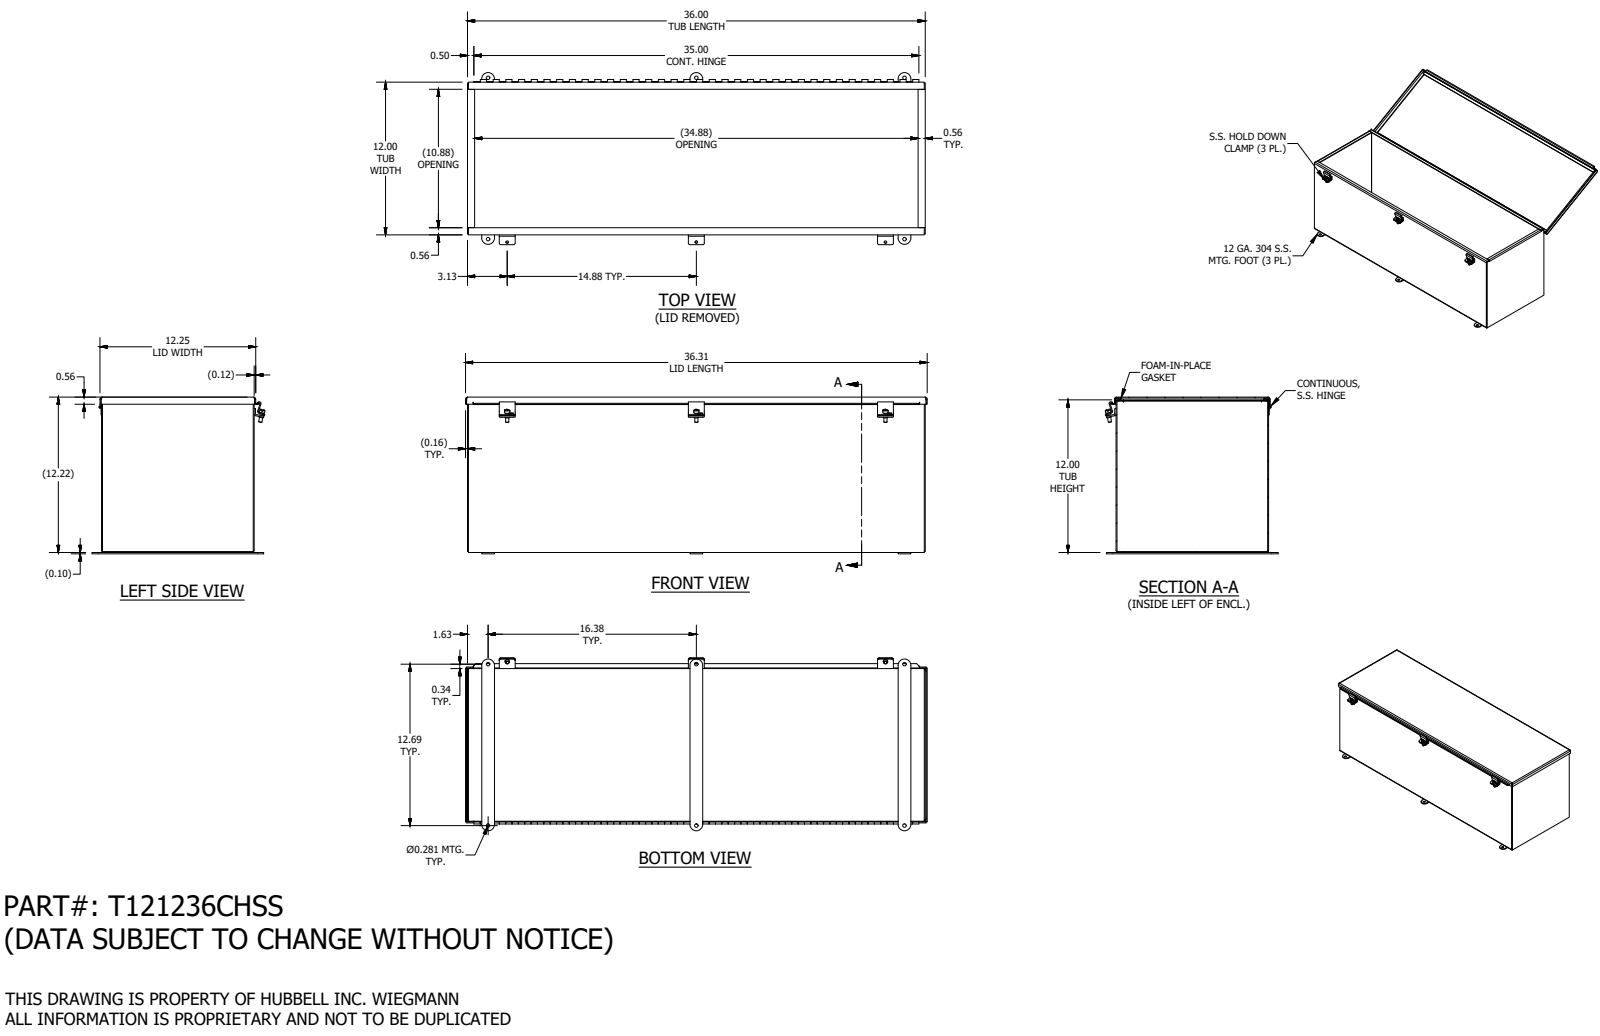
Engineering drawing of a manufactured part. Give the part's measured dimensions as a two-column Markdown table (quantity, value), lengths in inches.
| quantity | value |
| --- | --- |
| part name | T121236CHSS |
| STEP written by | SolidWorks 2019 (AUTOMOTIVE_DESIGN) |
| units | inches |
| bodies | 20 solids, 719 faces (431 planar, 249 cylindrical, 39 other) |
| overall size | 36.313 × 13.598 × 12.322 |
| volume | 171.3 in³ |
| surface area | 4 577 in² |
| round holes (diameter × count) | 0.11 × 6, 0.281 × 6, 0.196 × 3, 0.116 × 1 |
| round bosses / shafts (diameter × count) | 0.41 × 3, 0.344 × 3, 0.25 × 3, 0.2 × 1, 0.1 × 1 |
| partial cylindrical surfaces (radius × count) | 0.125 × 12, 0.094 × 11, 0.168 × 11, 0.085 × 8, 0.133 × 6, 0.5 × 6, 0.242 × 4, 0.063 × 3 |
| main face-to-face distances | 0.074, 11.926, 12.144, 11.852, 12, 12.218, 12.07, 35.926, 35.852, 36 |
| hole center spacings | 14.875, 16.375, 20.715, 0.75, 12.687, 14.875, 29.75, 32.75 |
